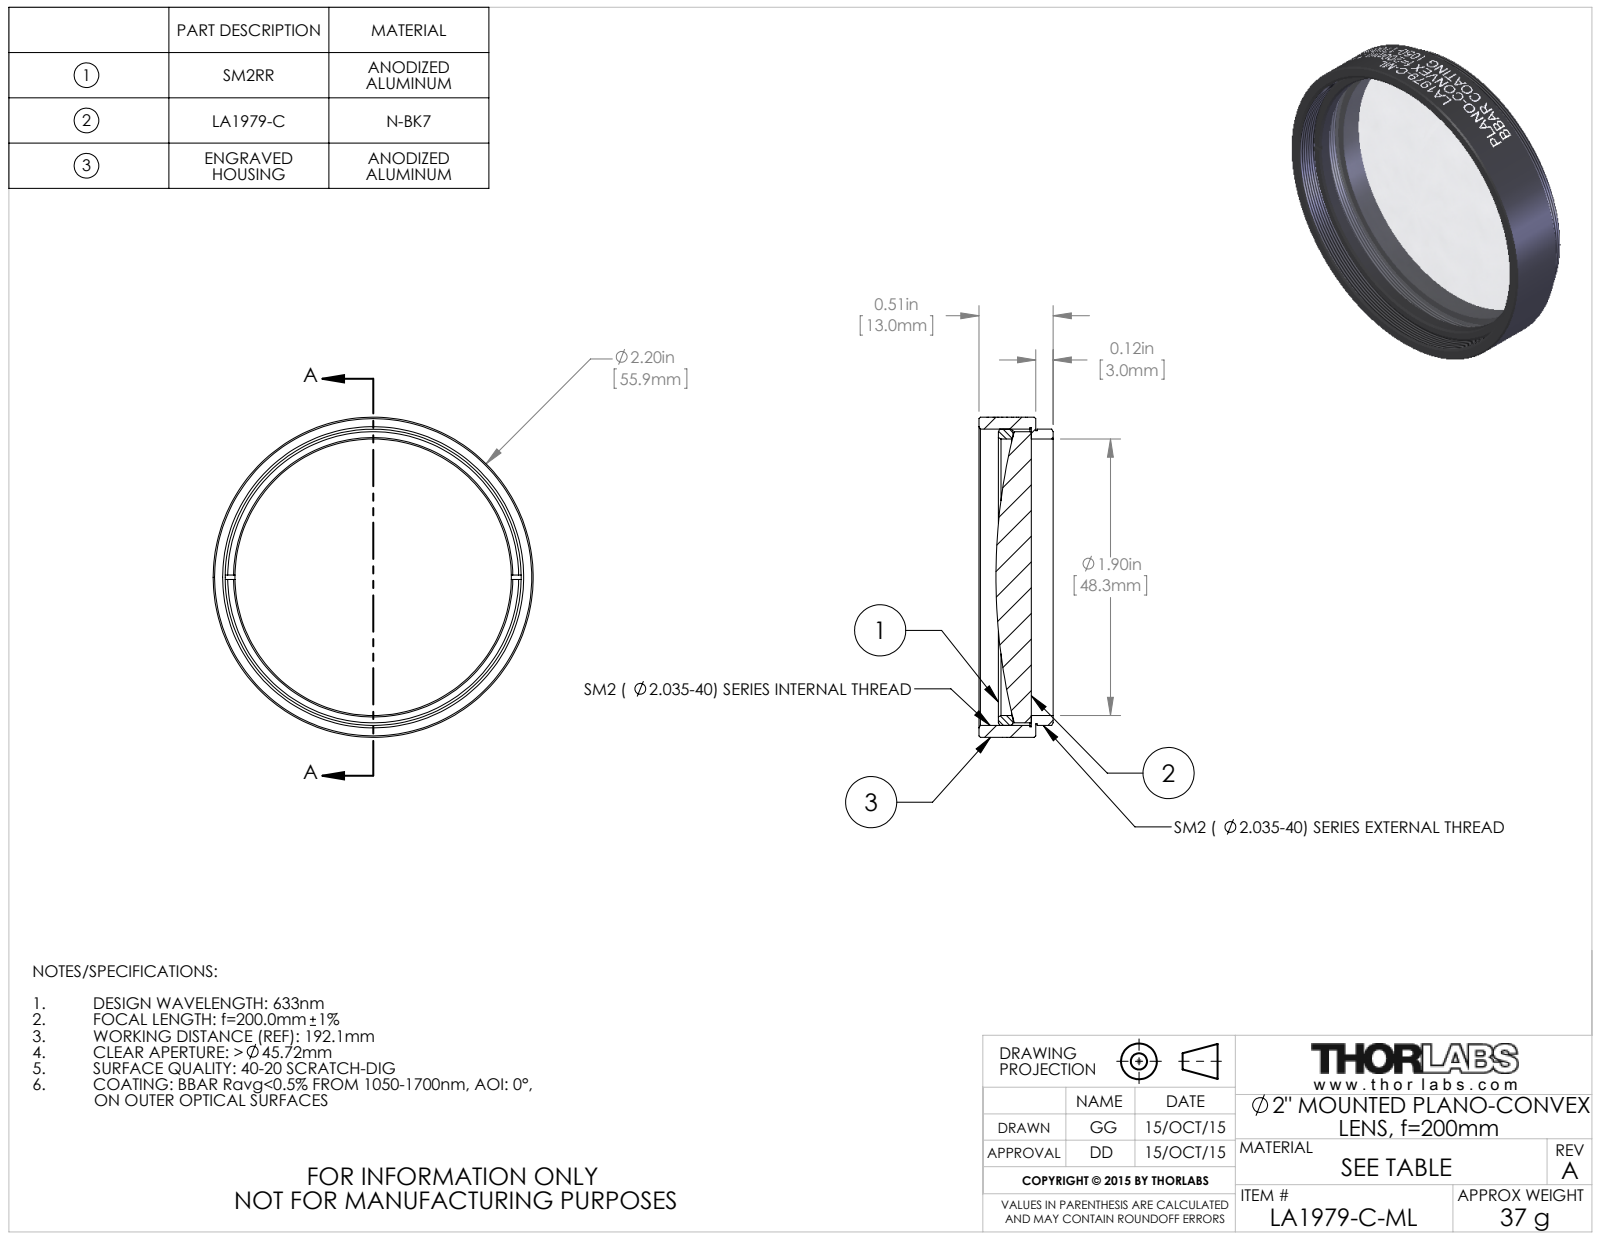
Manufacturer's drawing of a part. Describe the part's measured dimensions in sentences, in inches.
The part is named "TTN039675-E0W". Its 3-D file was written by "SolidWorks 2014 (CONFIG_CONTROL_DESIGN)". It is 3 solids with 149 faces: 16 planar, 109 cylindrical and 24 other. Overall it measures 2.2 by 2.2 by 0.51 inches. Its volume is 0.882 cubic inches and its surface area 17.62 square inches. Round holes: 1 of diameter 1.9, 1 of diameter 2.055. Round bosses or shafts: 1 of diameter 2.2, 1 of diameter 2.035, 1 of diameter 2.015, 1 of diameter 2. The main face-to-face distances are 0.03, 0.39, 0.36, 0.12, 0.15, 0.51, 0.276, 0.156, 0.126, 0.234.
